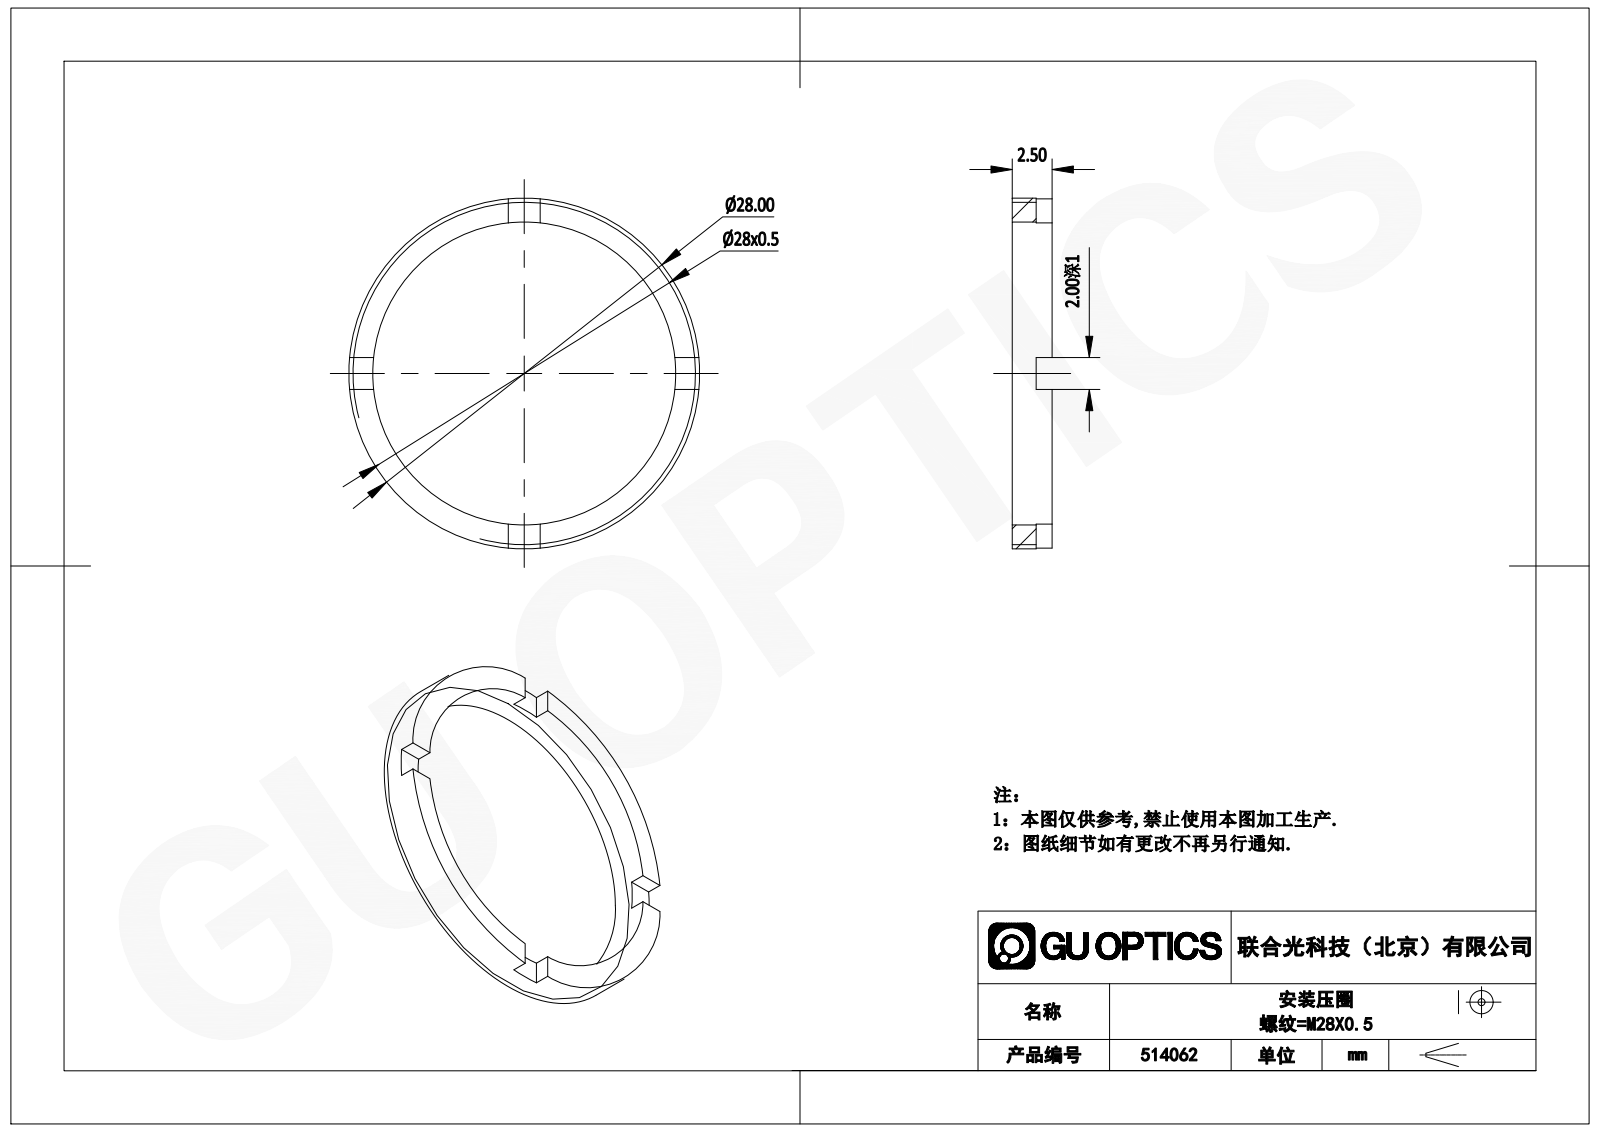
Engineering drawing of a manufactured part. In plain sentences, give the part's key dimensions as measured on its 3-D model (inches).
The part is named "514062". Its 3-D file was written by "SolidWorks 2020 (CONFIG_CONTROL_DESIGN)". It is 1 solid with 21 faces: 17 planar, 4 cylindrical and 0 other. Overall it measures 1.102 by 1.102 by 0.098 inches. Its volume is 0.018 cubic inches and its surface area 1.03 square inches. Round holes: 1 of diameter 0.984. Round bosses or shafts: 1 of diameter 1.102. The main face-to-face distances are 0.098, 0.059, 0.039, 0.079.
